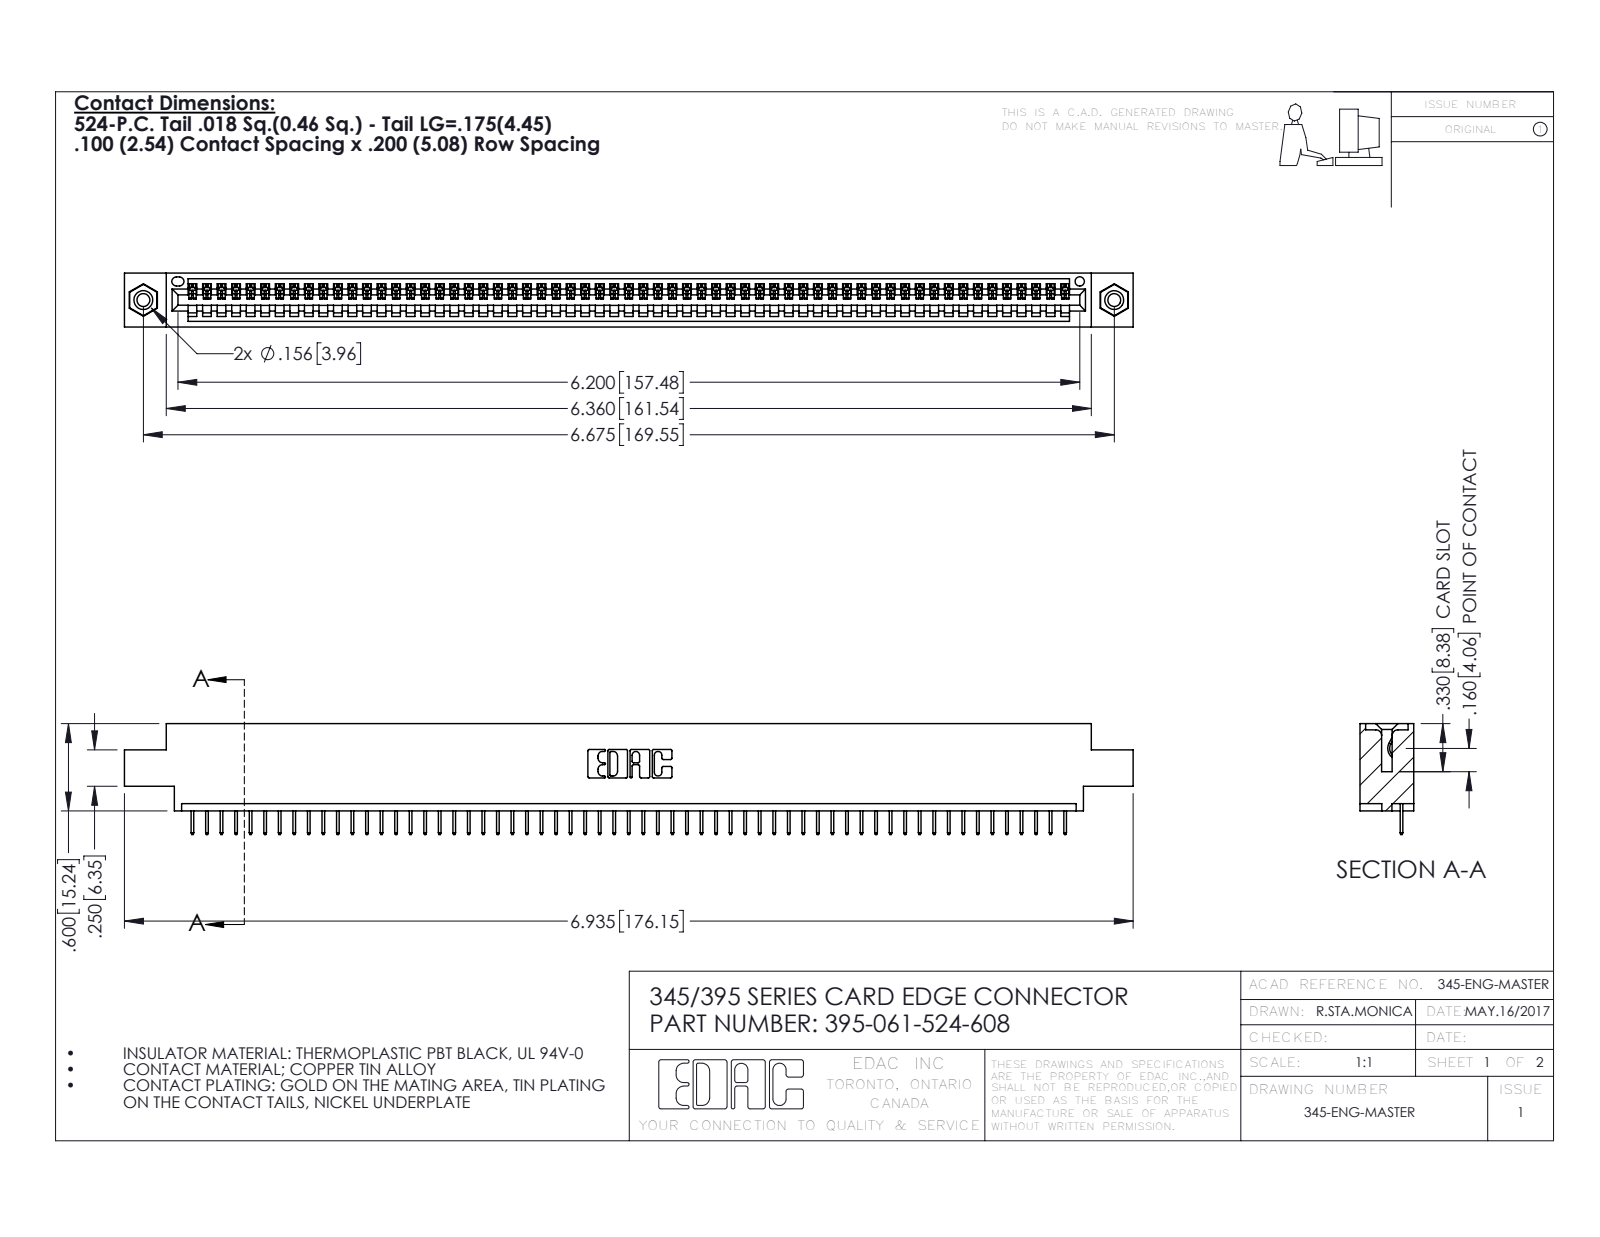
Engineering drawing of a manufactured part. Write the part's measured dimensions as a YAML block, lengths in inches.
part_name: "395-061-524-608; 345-250-001_345-250-003-102; 345 Part_0.170 Offset - 0.156 Dia-TI; 345-292-001_345-293-124"
step_written_by: "SolidWorks 2016 (CONFIG_CONTROL_DESIGN)"
units: inches
bodies: {solids: 64, faces: 3972, planar: 2922, cylindrical: 1034, other: 16}
overall_size: [6.935, 0.762, 0.37]
volume: 1.008
surface_area: 33.47
round_holes:
  - {diameter: 0.089, count: 2}
  - {diameter: 0.125, count: 2}
  - {diameter: 0.156, count: 2}
  - {diameter: 0.064, count: 1}
round_bosses_or_shafts:
  - {diameter: 0.155, count: 2}
partial_cylinders:
  - {radius: 0.006, count: 122}
  - {radius: 0.01, count: 22}
  - {radius: 0.007, count: 6}
  - {radius: 0.031, count: 6}
  - {radius: 0.026, count: 3}
  - {radius: 0.031, count: 2}
  - {radius: 0.04, count: 2}
  - {radius: 0.014, count: 1}
face_to_face_distances: [0.072, 0.298, 0.37, 0.2, 0.098, 0.272, 0.025, 0.225, 0.072, 0.175]
hole_center_spacings: [0.27, 6.439, 6.675]
